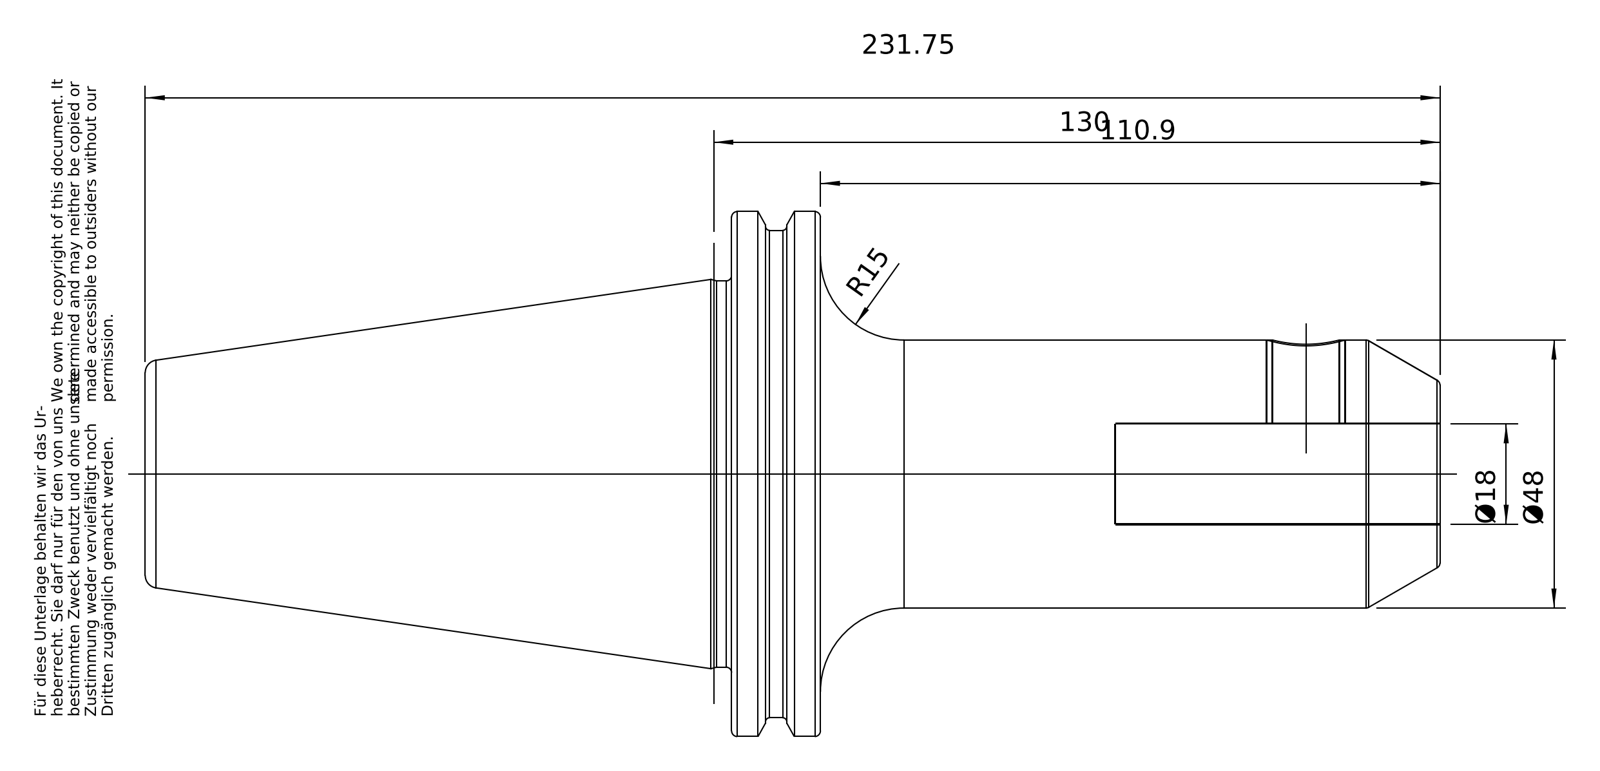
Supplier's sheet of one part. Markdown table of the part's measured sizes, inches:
| quantity | value |
| --- | --- |
| part name | 50-304-18 |
| STEP written by | PRO/ENGINEER BY PARAMETRIC TECHNOLOGY CORPORATION, 2010430 (CONFIG_CONTROL_DESIGN) |
| units | inches |
| bodies | 1 solid, 104 faces (22 planar, 32 cylindrical, 50 other) |
| overall size | 9.118 × 3.837 × 3.701 |
| volume | 32.06 in³ |
| surface area | 95.79 in² |
| round holes (diameter × count) | 0.472 × 1, 0.551 × 1, 0.709 × 1, 0.817 × 1, 0.985 × 1, 1.012 × 1 |
| round bosses / shafts (diameter × count) | 3.583 × 1, 2.722 × 1, 1.89 × 1, 0.945 × 1 |
| partial cylindrical surfaces (radius × count) | 0.069 × 5, 1.919 × 1 |
| main face-to-face distances | 0.624, 4.992, 4.368, 4.126, 4.75, 9.118, 2.866, 6.831, 2.705, 2.081 |
